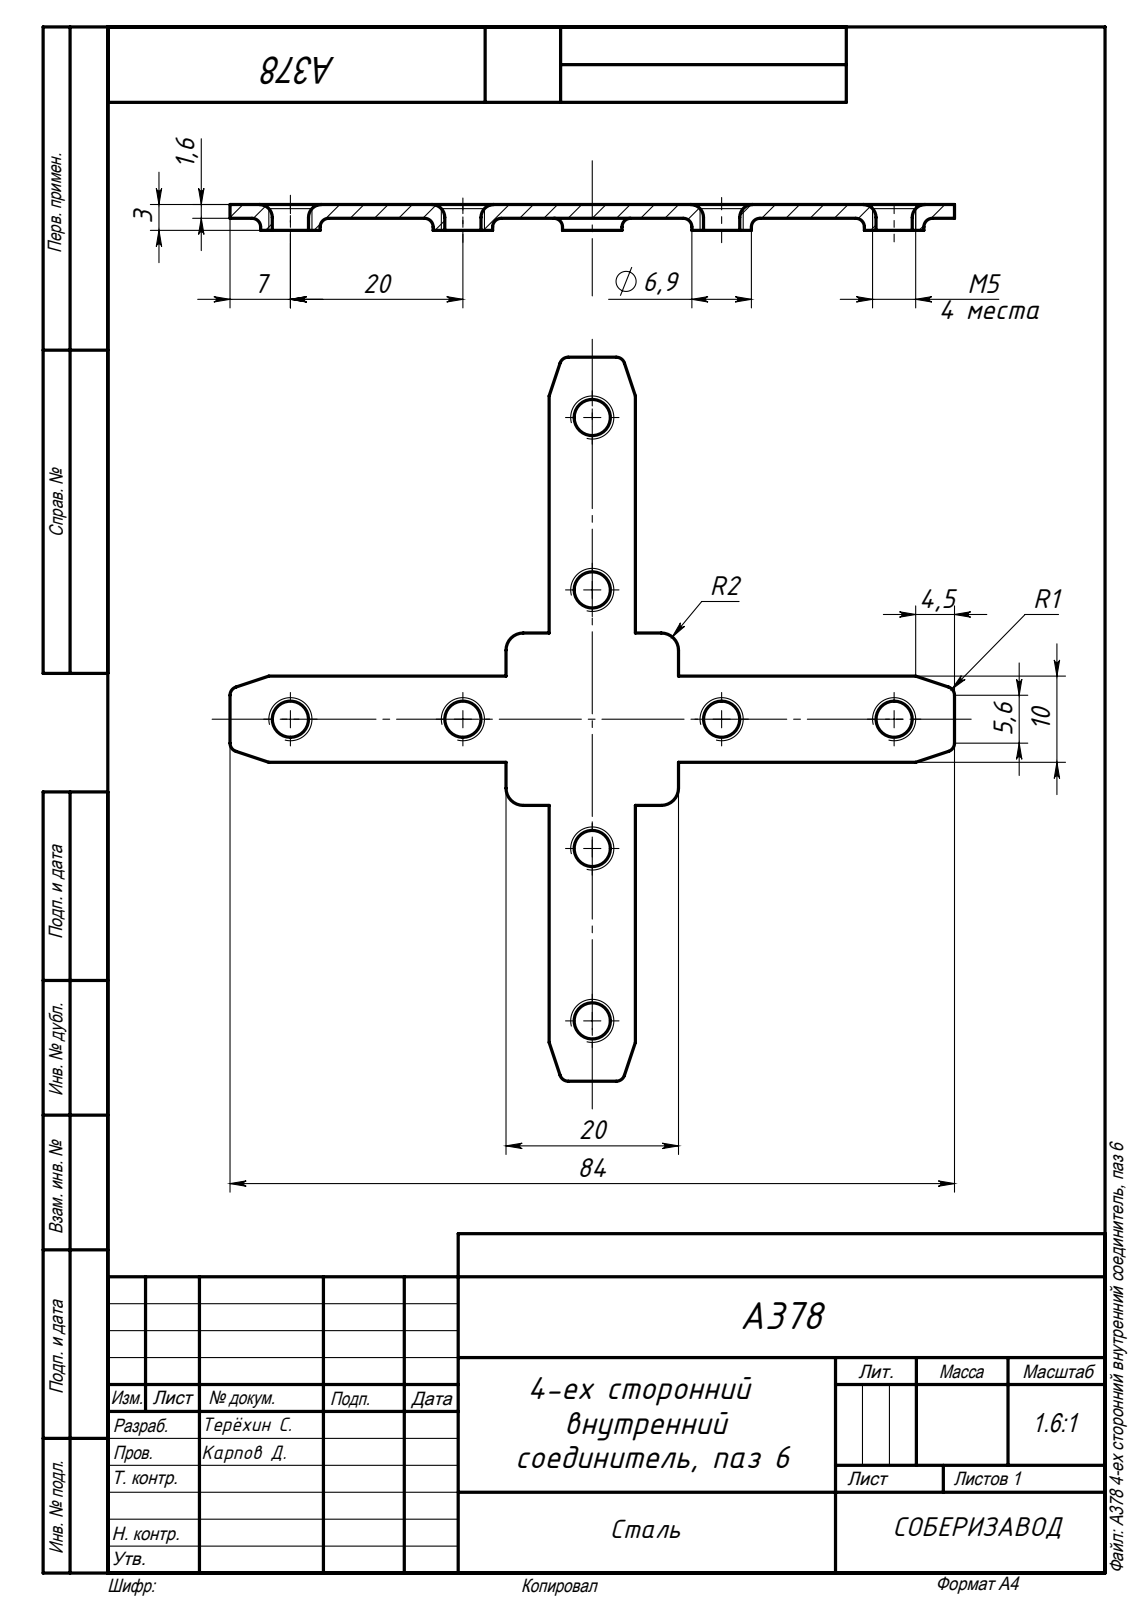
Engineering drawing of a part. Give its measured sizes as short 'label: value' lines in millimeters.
name: A378 4-ех сторонний внутренний соединитель, паз 6
written by: SolidWorks 2020 (AUTOMOTIVE_DESIGN)
unit: mm
bodies: 1 solid, 114 faces (38 planar, 44 cylindrical, 32 other)
size: 84 × 84 × 3
volume: 2 705 mm³; area: 4 018 mm²
holes: 8× ⌀4.2
bosses: 8× ⌀6.9
rounds: 8× R1, 4× R2
face distances: 1.6, 1.4, 3, 10, 5, 15, 32, 37, 47, 52
hole spacings: 38.08, 20, 21.21, 49.5, 50, 30, 70
